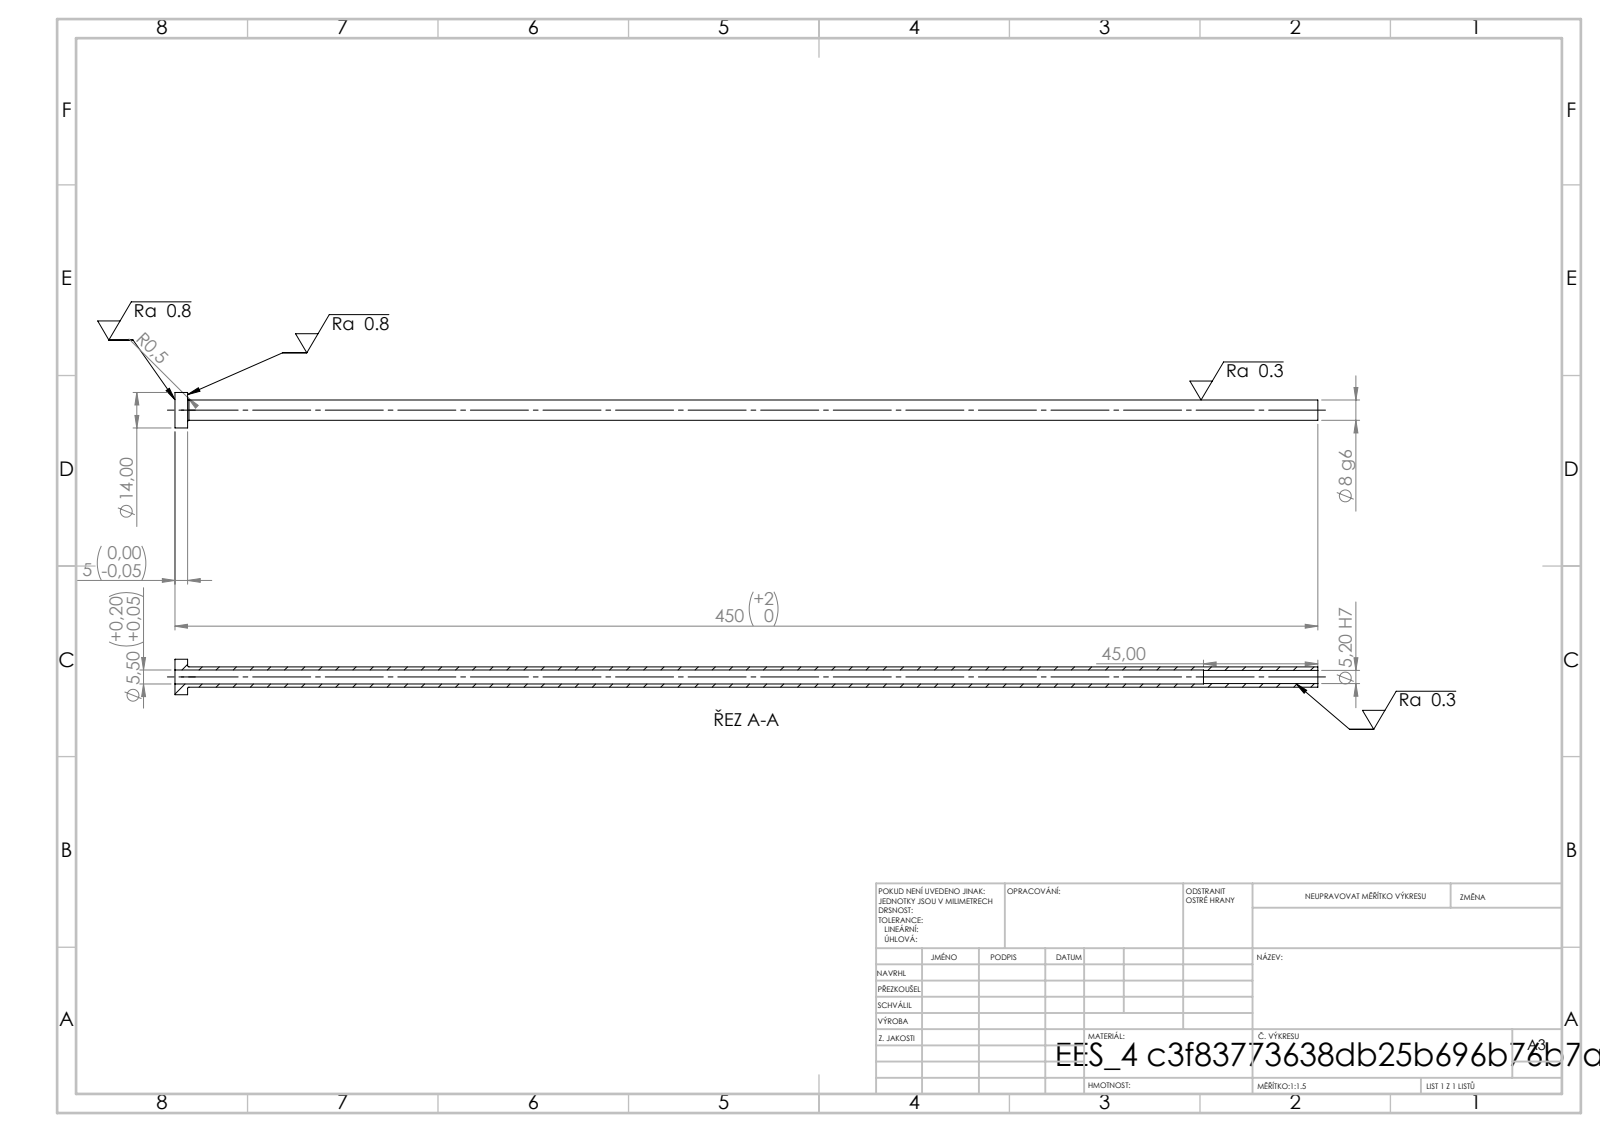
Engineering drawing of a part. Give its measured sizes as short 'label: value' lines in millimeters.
written by: SolidWorks 2019 (CONFIG_CONTROL_DESIGN)
unit: mm
bodies: 1 solid, 14 faces (4 planar, 8 cylindrical, 2 other)
size: 450 × 14 × 14
volume: 12 561 mm³; area: 19 397 mm²
holes: 1× ⌀5.2, 1× ⌀5.5
bosses: 1× ⌀14, 1× ⌀8
face distances: 5, 450, 445, 405, 400, 45
